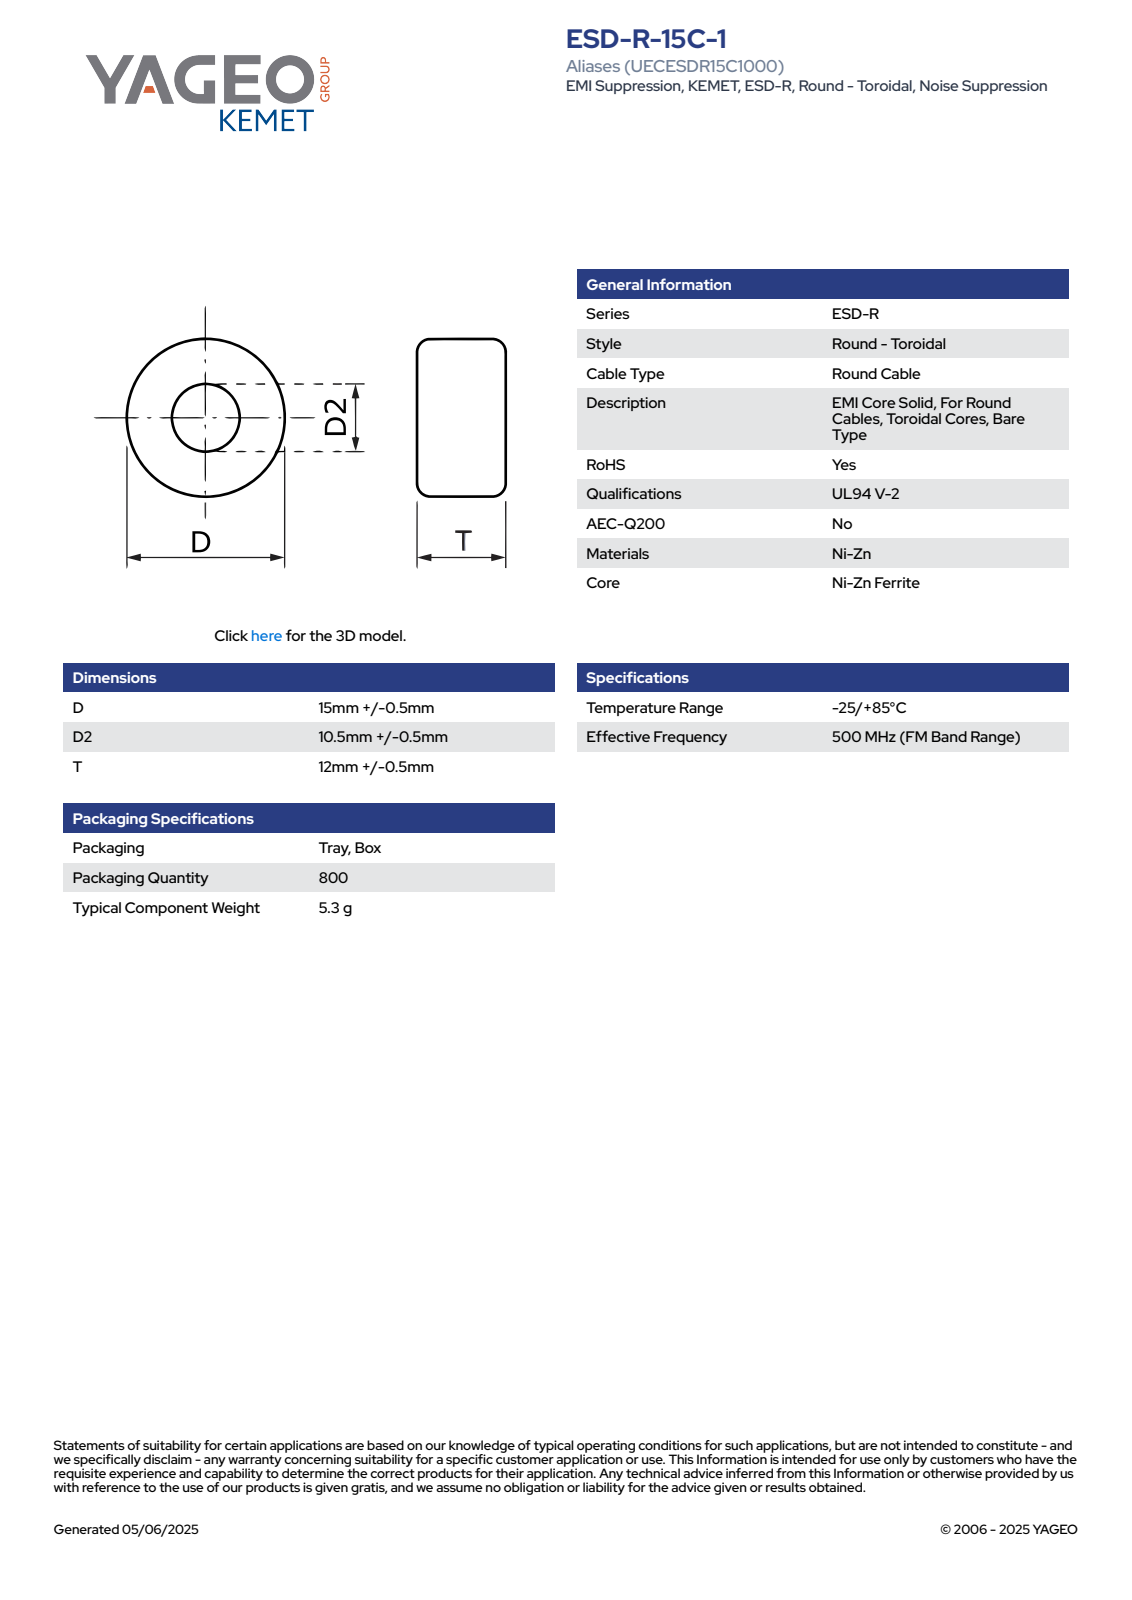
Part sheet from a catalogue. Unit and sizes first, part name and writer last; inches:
Units: inches
Overall size (bounding box): 0.611 × 0.61 × 0.492
Round holes (diameter × count): ⌀0.413 ×1
Round bosses / shafts (diameter × count): ⌀0.61 ×1
Partial cylindrical surfaces — rounded edges, fillets, slot ends (radius × count): R0.306 ×1
Main face-to-face distances: 0.492, 0.213, 0.28, 0.067, 0.013, 0.225, 0.267, 0.054, 0.042, 0.254
Volume: 0.078 in³ · Surface area: 1.871 in²
Bodies: 1 solid, 66 faces (24 planar, 7 cylindrical, 35 other)
Part name (STEP PRODUCT): EC_KBC_D15.5D210.5T12.5
STEP written by: SolidWorks 2021 (AUTOMOTIVE_DESIGN)
